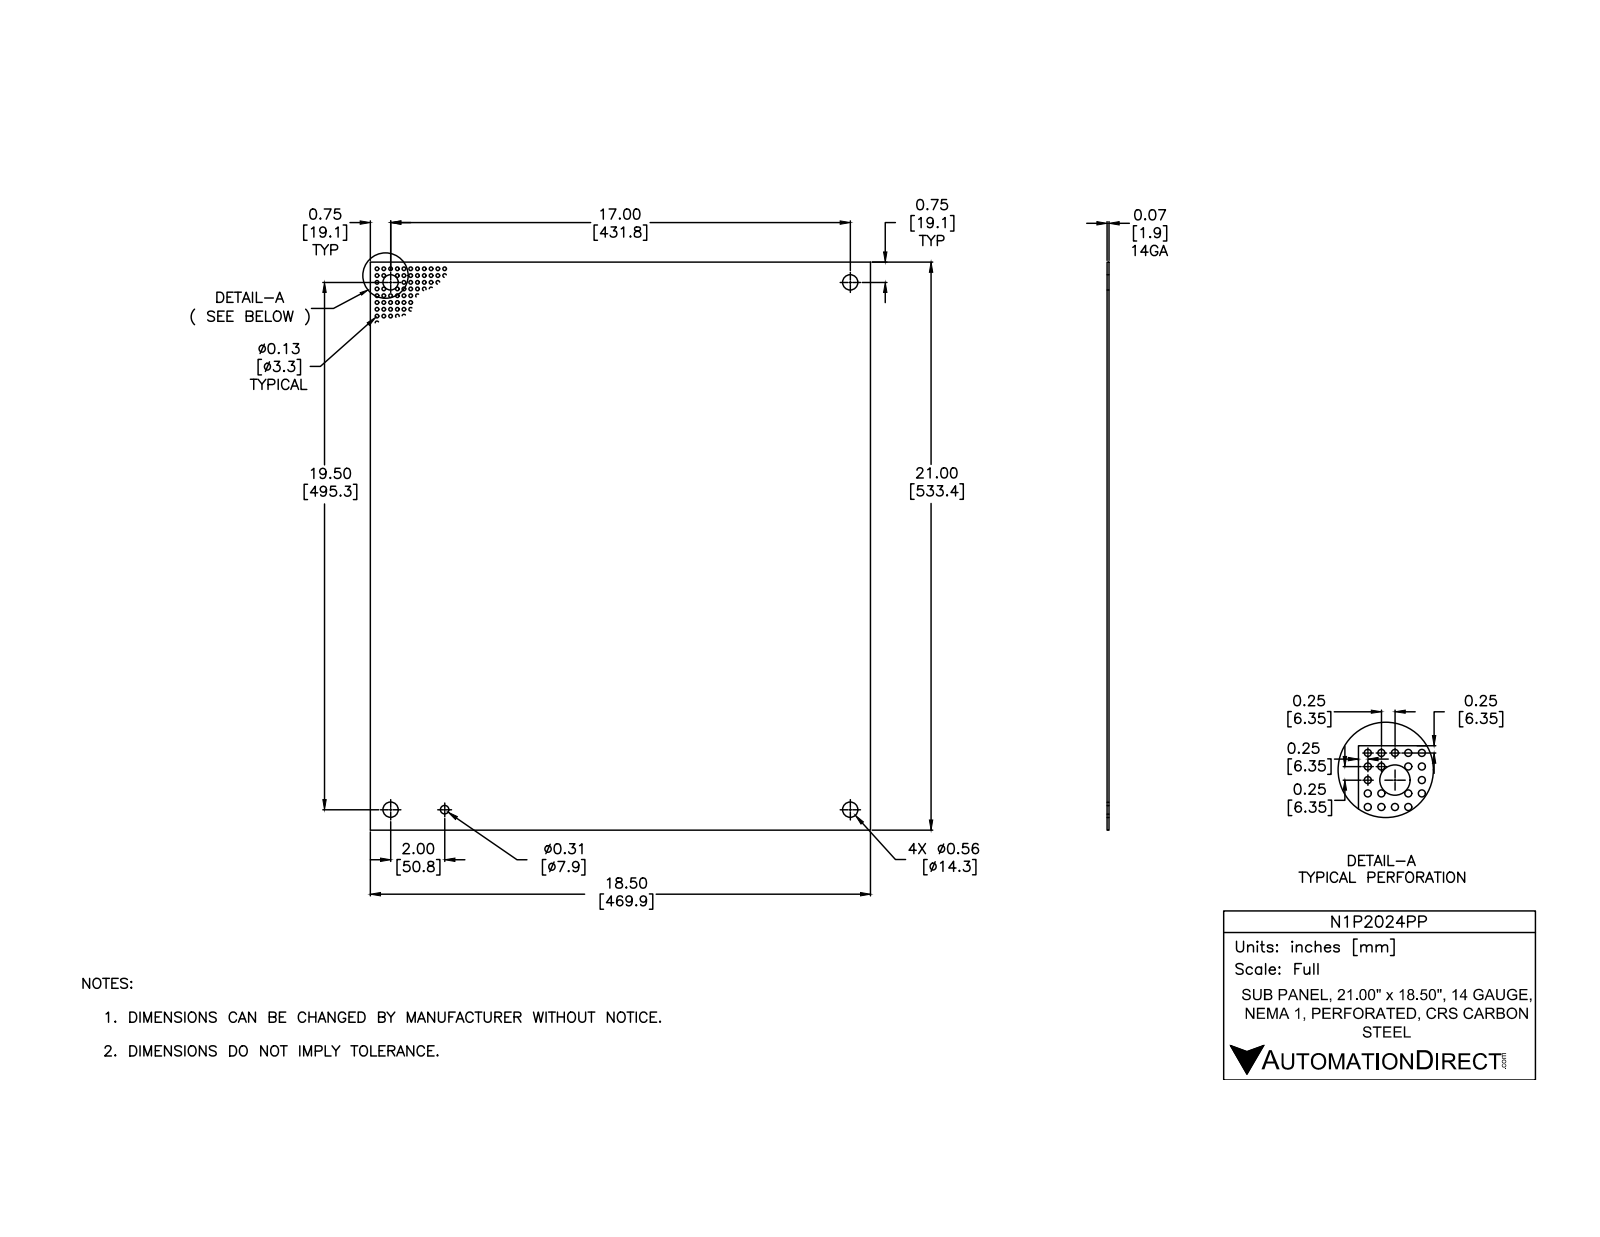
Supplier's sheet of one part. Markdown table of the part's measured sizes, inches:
| quantity | value |
| --- | --- |
| part name | N1P_PP-LARGE |
| STEP written by | Autodesk Inventor 2012 (AUTOMOTIVE_DESIGN) |
| units | inches |
| bodies | 1 solid, 11 faces (6 planar, 5 cylindrical, 0 other) |
| overall size | 21 × 18.5 × 0.074 |
| volume | 28.67 in³ |
| surface area | 781.3 in² |
| round holes (diameter × count) | 0.563 × 4, 0.312 × 1 |
| main face-to-face distances | 0.074, 18.5, 21 |
| hole center spacings | 17, 19.5, 25.87, 2, 15, 19.602, 24.602 |
